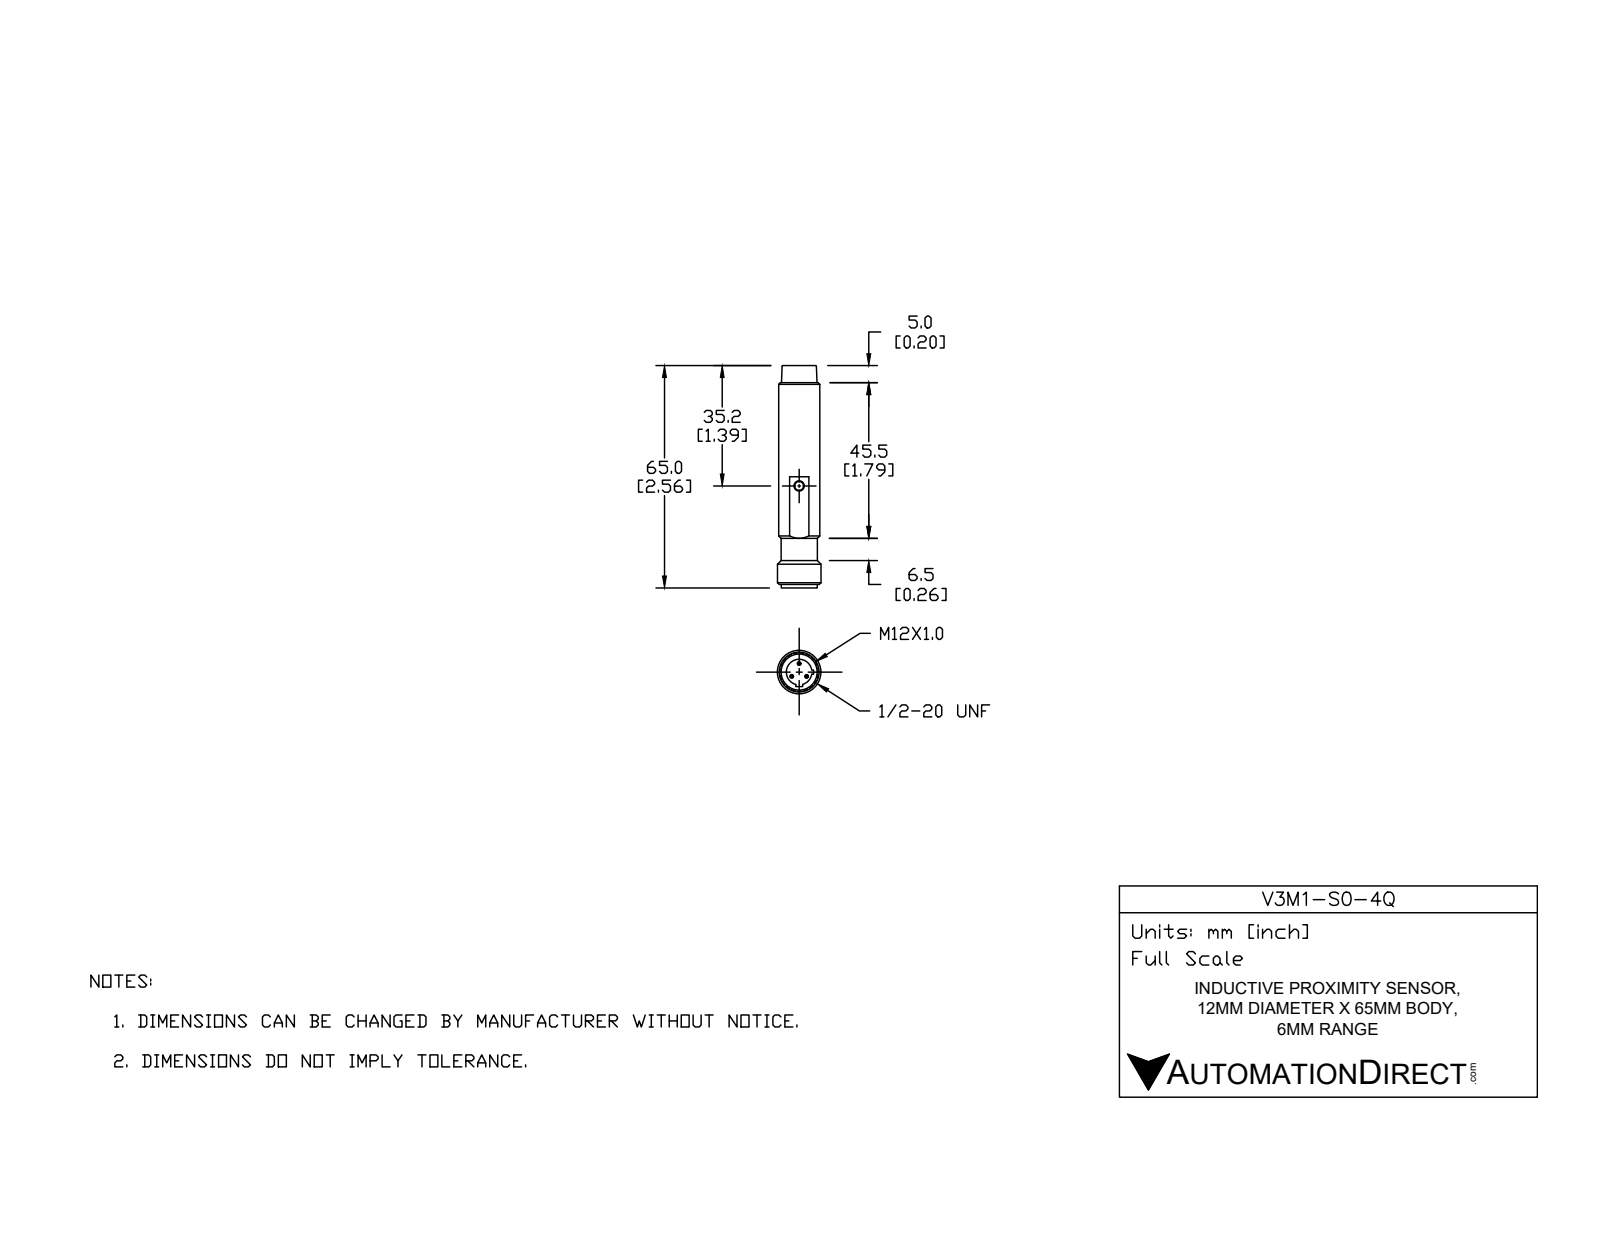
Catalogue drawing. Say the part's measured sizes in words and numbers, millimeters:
The part is named "V3M1_4Q_fig". Its 3-D file was written by "ST-DEVELOPER v16.7 (AUTOMOTIVE_DESIGN)". It is 3 solids with 52 faces: 25 planar, 16 cylindrical and 11 other. Overall it measures 65 by 12.7 by 12.7 millimeters. Its volume is 6 688 cubic millimeters and its surface area 3 189 square millimeters. Round holes: 3 of diameter 1, 1 of diameter 2.6, 1 of diameter 7.5, 1 of diameter 9.5. Round bosses or shafts: 3 of diameter 0.98, 1 of diameter 12.7, 1 of diameter 12, 1 of diameter 10.6, 1 of diameter 10.5, 1 of diameter 9.55, 1 of diameter 9.4. The main face-to-face distances are 57.9, 65, 7.1, 1, 64, 6.1, 9.5, 5, 52.9, 59. The hole center spacings are 2.5, 4.33, 4.34.
